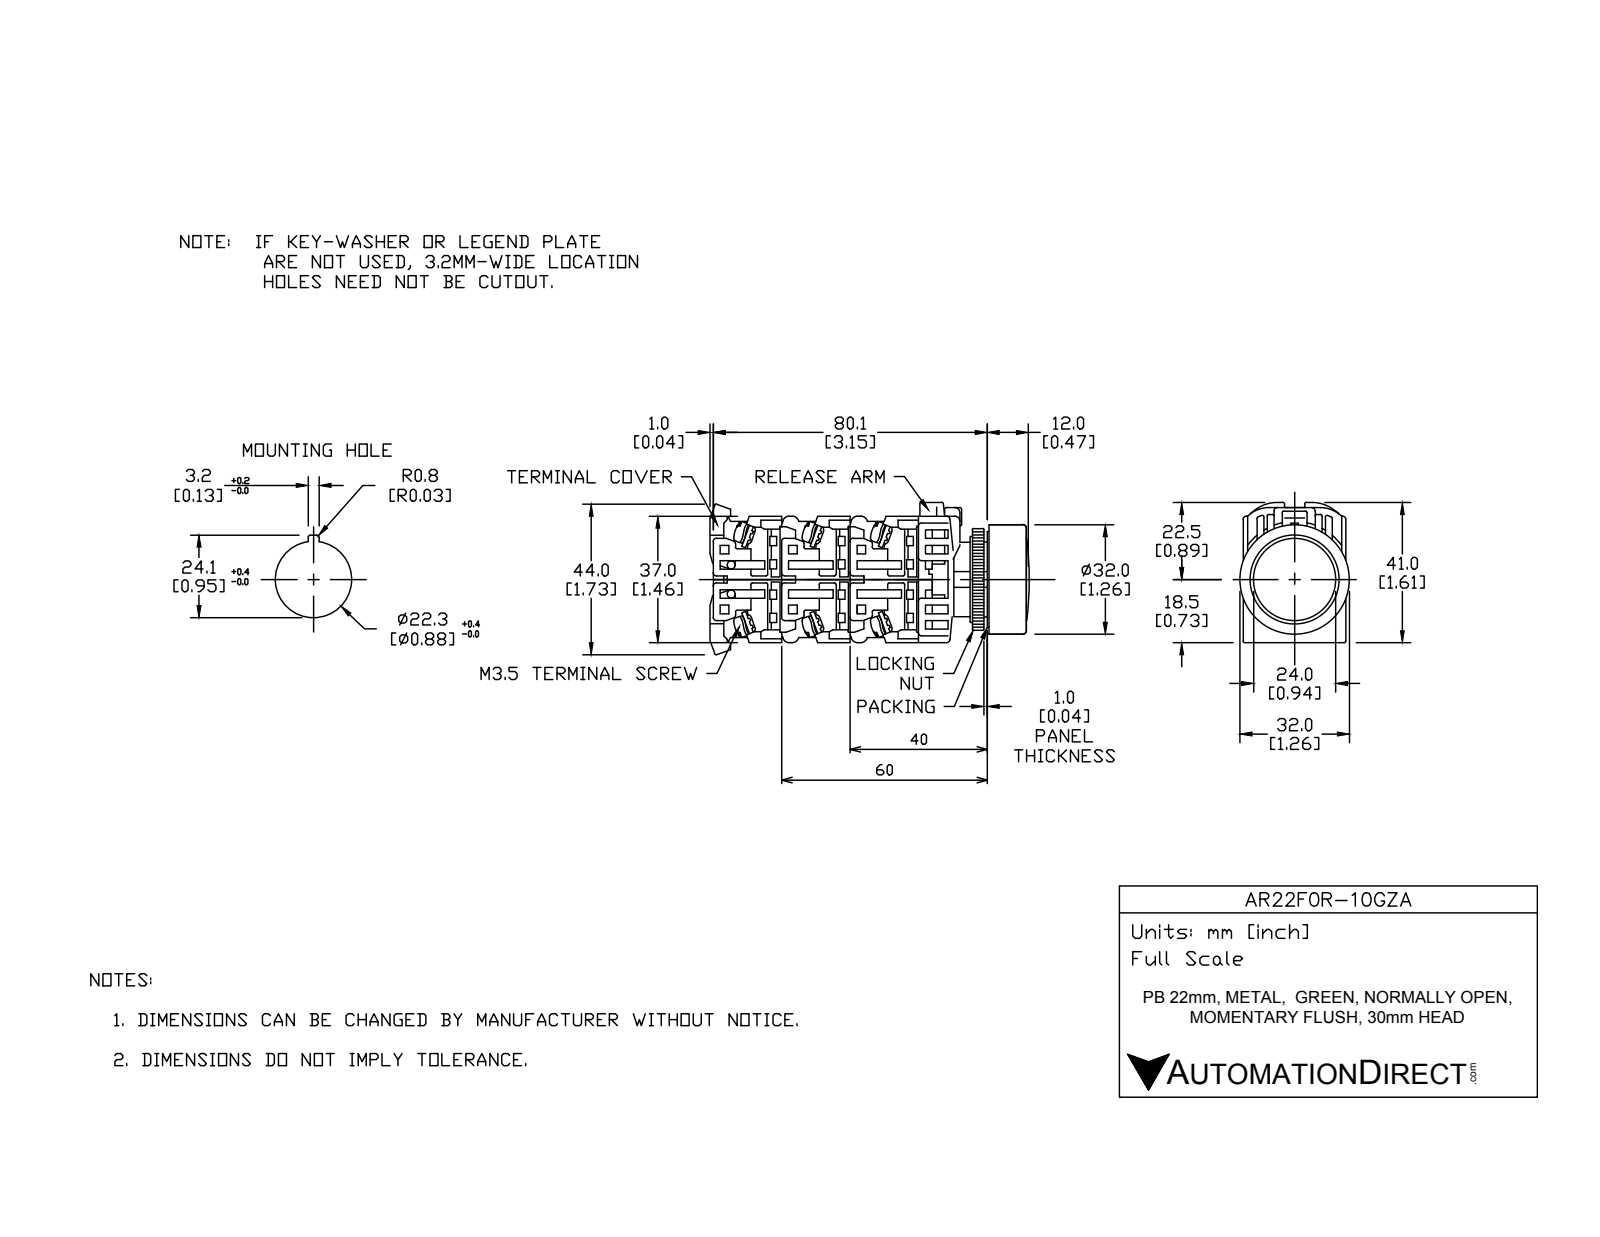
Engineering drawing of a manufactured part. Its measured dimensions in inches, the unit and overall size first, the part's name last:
Units: inches
Overall size (bounding box): 2.077 × 1.614 × 1.26
Round holes (diameter × count): ⌀0.858 ×1, ⌀0.866 ×1, ⌀0.984 ×1, ⌀1.22 ×1
Round bosses / shafts (diameter × count): ⌀0.197 ×2, ⌀1.26 ×1, ⌀1.201 ×1, ⌀1.173 ×1, ⌀0.945 ×1, ⌀0.937 ×1, ⌀0.856 ×1, ⌀0.669 ×1
Partial cylindrical surfaces — rounded edges, fillets, slot ends (radius × count): R0.02 ×23, R0.069 ×4, R0.197 ×4, R0.157 ×2, R0.653 ×1, R0.693 ×1
Main face-to-face distances: 0.039, 1.122, 0.709, 0.118, 0.079, 1.142, 1.181, 0.413, 0.315, 0.807
Volume: 1.669 in³ · Surface area: 30.06 in²
Bodies: 12 solids, 295 faces (201 planar, 74 cylindrical, 20 other)
Part name (STEP PRODUCT): AR22F0R-10GZA
STEP written by: SolidWorks 2017 (AUTOMOTIVE_DESIGN)
